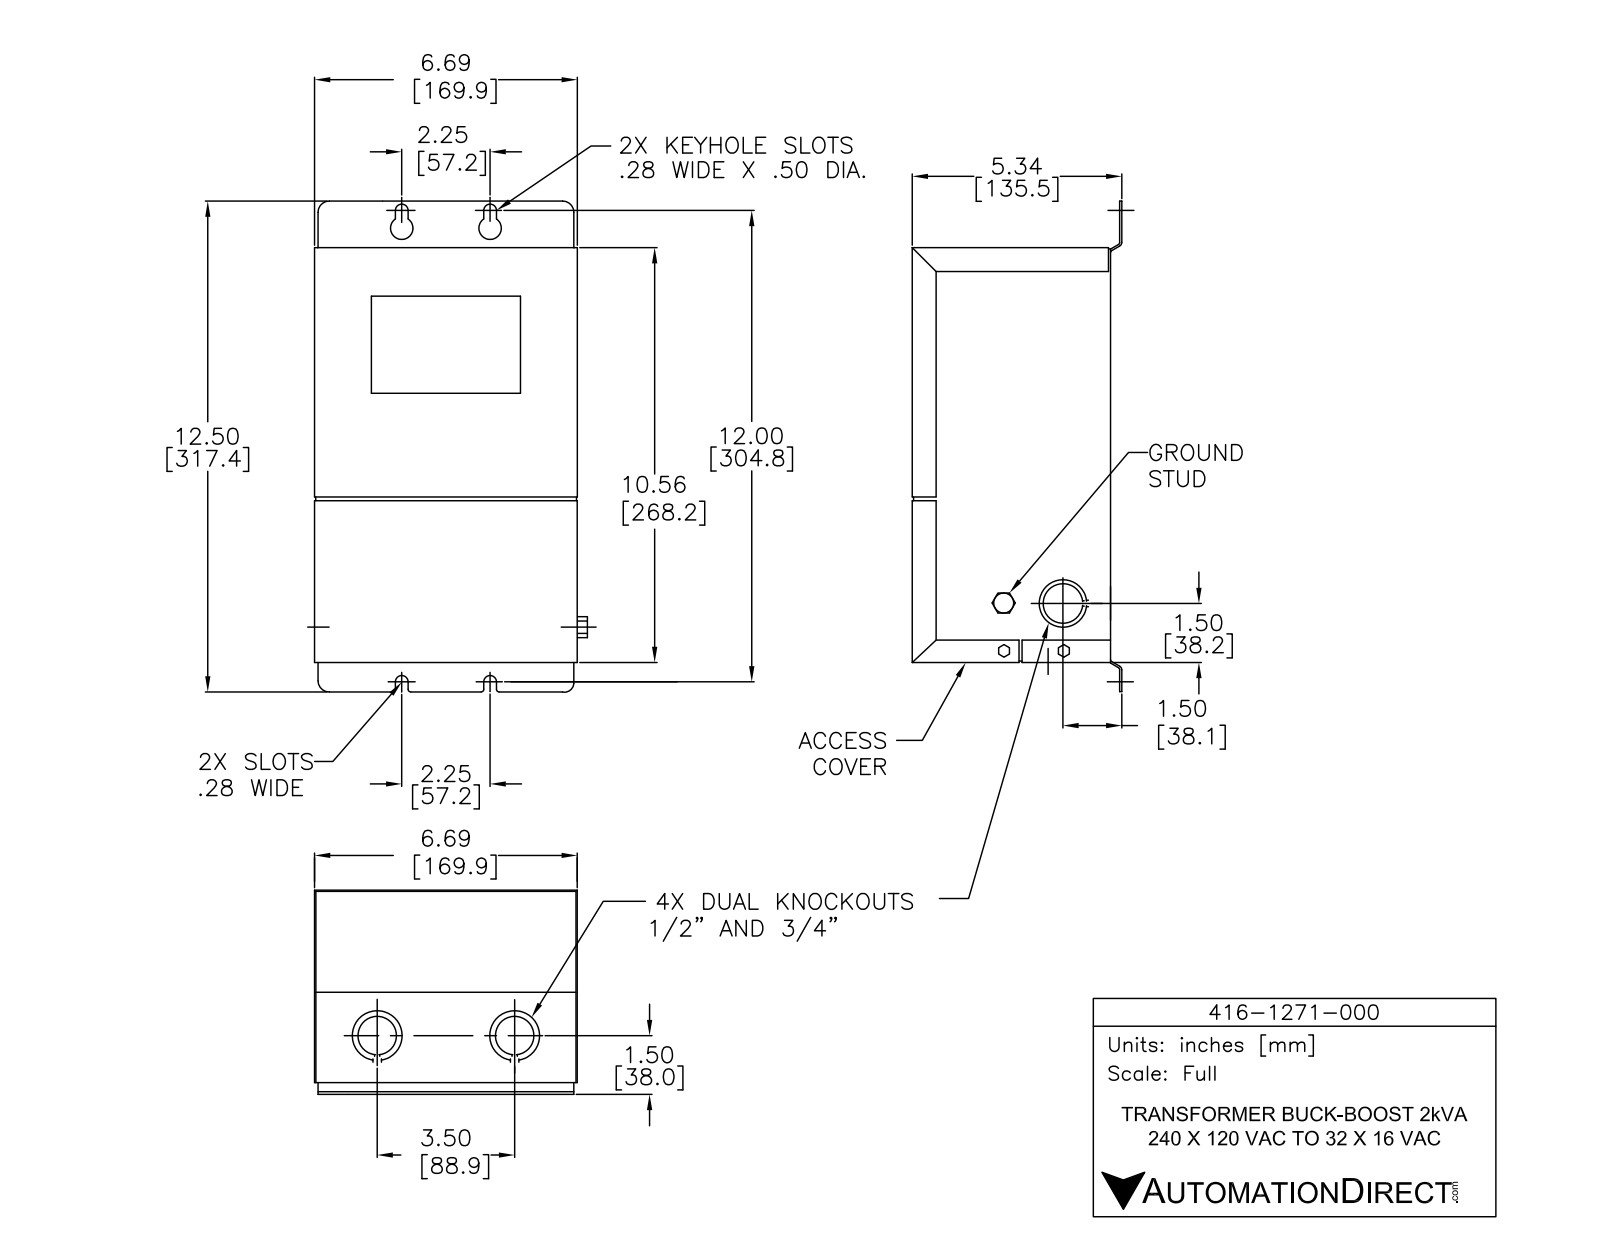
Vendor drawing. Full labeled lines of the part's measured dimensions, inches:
Part name (STEP PRODUCT): 416-1271-000
STEP written by: SolidWorks 2013 (AUTOMOTIVE_DESIGN)
Units: inches
Bodies: 1 solid, 186 faces (114 planar, 64 cylindrical, 8 other)
Overall size (bounding box): 12.5 × 6.9 × 5.341
Volume: 362.1 in³ · Surface area: 348.2 in²
Round holes (diameter × count): ⌀0.5 ×2, ⌀0.875 ×2, ⌀0.24 ×1, ⌀0.29 ×1, ⌀0.875 ×1
Round bosses / shafts (diameter × count): ⌀1.11 ×2, ⌀1.125 ×1
Partial cylindrical surfaces — rounded edges, fillets, slot ends (radius × count): R0.04 ×10, R0.25 ×10, R0.14 ×5, R0.08 ×2, R0.1 ×1, R0.167 ×1, R0.207 ×1
Main face-to-face distances: 5.12, 6.62, 0.04, 10.64, 6.66, 5.121, 6.7, 5.3, 0.18, 5.301
Hole centre spacings: 1.361, 1.371, 2.25, 2.35, 3.5
